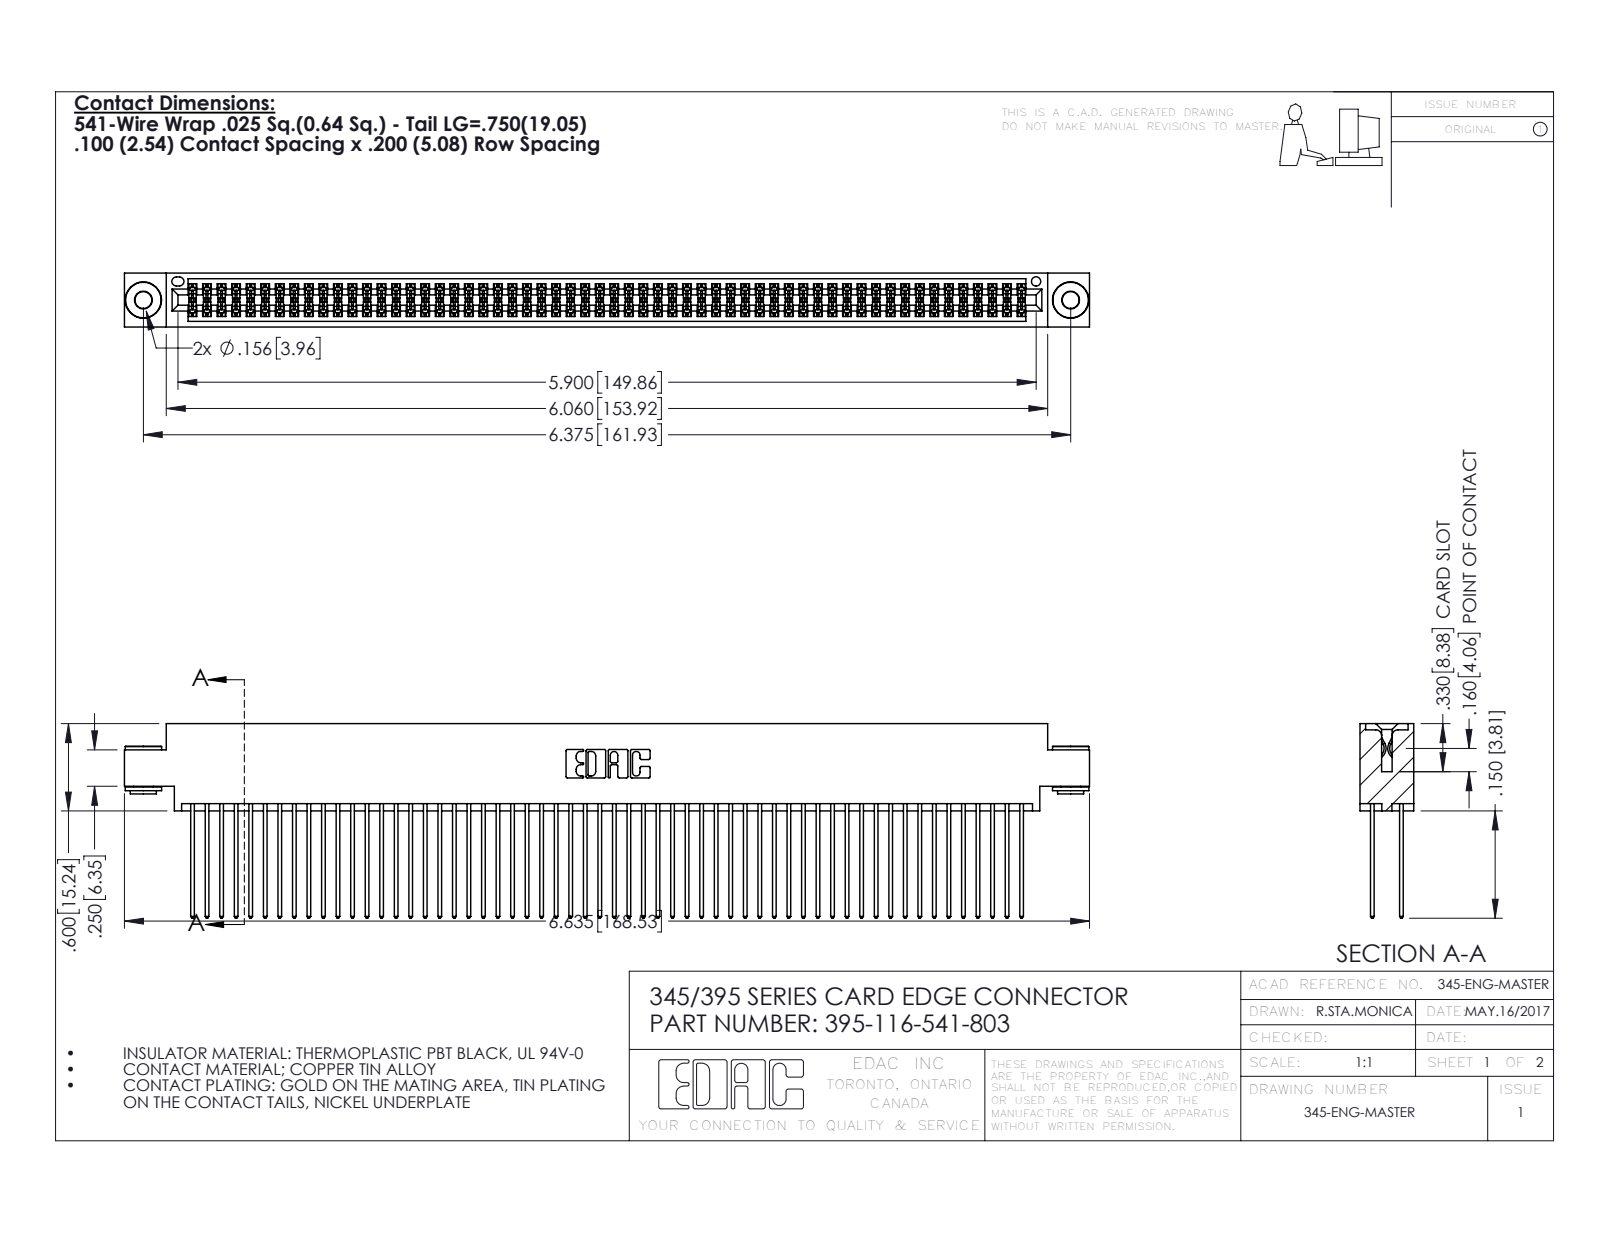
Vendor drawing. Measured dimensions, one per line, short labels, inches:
name: 345 Part_0.170 Offset - 0.156 Dia-TH; 395-116-541-803; 345-250-002_345-250-002-102; 345-292-001_345-293-141
written by: SolidWorks 2016 (CONFIG_CONTROL_DESIGN)
unit: in
bodies: 119 solids, 5968 faces (3922 planar, 2038 cylindrical, 8 other)
size: 6.635 × 1.337 × 0.37
volume: 1.043 in³; area: 45.03 in²
holes: 2× ⌀0.116, 2× ⌀0.156, 1× ⌀0.064
bosses: 2× ⌀0.25, 2× ⌀0.18, 2× ⌀0.136
rounds: 174× R0.006, 116× R0.01, 22× R0.01, 6× R0.007, 6× R0.031, 3× R0.026, 2× R0.014, 2× R0.019
face distances: 0.072, 0.298, 0.2, 0.098, 0.272, 0.025, 0.225, 0.37, 0.175, 0.149
hole spacings: 0.27, 6.139, 6.375
